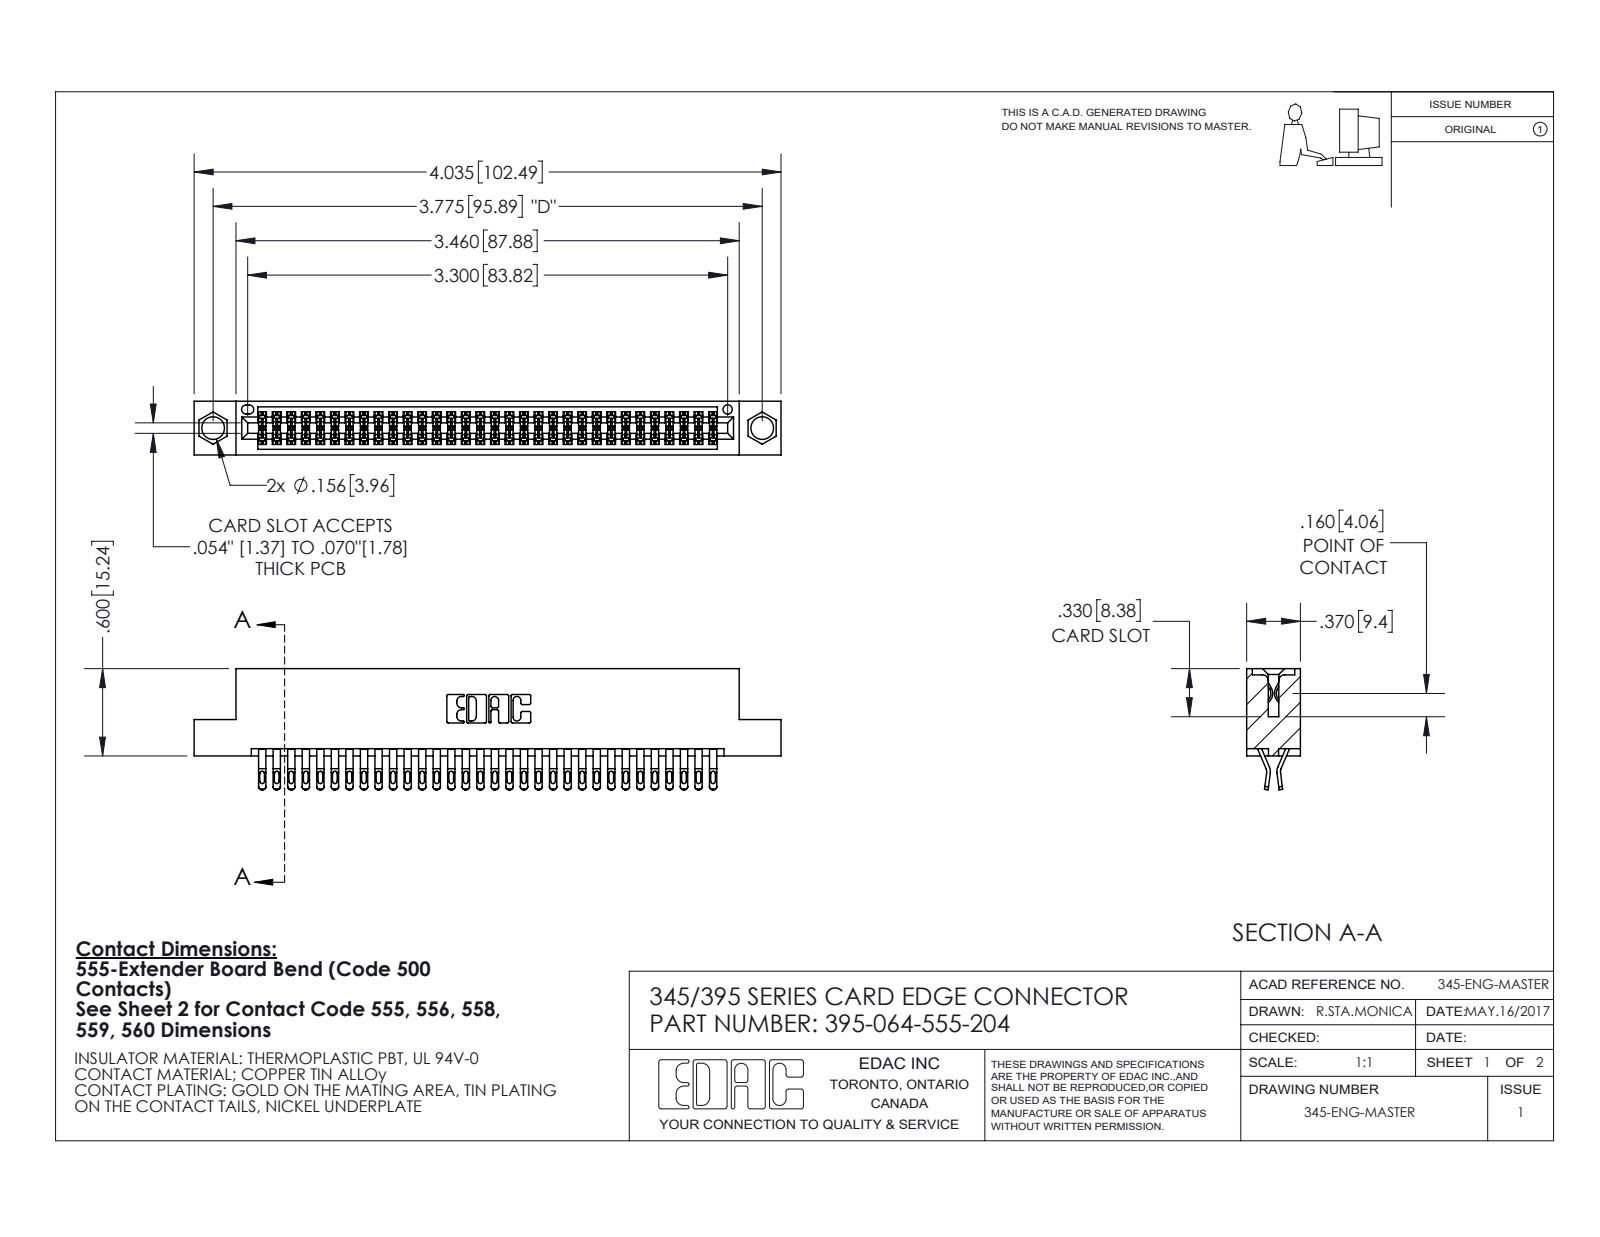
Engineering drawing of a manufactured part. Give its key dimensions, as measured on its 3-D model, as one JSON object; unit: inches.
{"part_name": "395-064-555-204; 345-292-001_555 Tail; 345 Part_Flush Mounting Lugs - 0.156 Dia-TI", "step_written_by": "SolidWorks 2020 (CONFIG_CONTROL_DESIGN)", "units": "inches", "bodies": {"solids": 65, "faces": 3724, "planar": 2078, "cylindrical": 1646, "other": 0}, "overall_size": [4.035, 0.832, 0.37], "volume_in3": 0.607, "surface_area_in2": 23.25, "round_holes": [[0.156, 2], [0.064, 1]], "partial_cylinders_radius": [[0.016, 160], [0.02, 128], [0.006, 96], [0.01, 22], [0.007, 6], [0.031, 6], [0.026, 3], [0.01, 2]], "face_to_face_distances": [0.298, 0.072, 0.2, 0.37, 0.025, 0.098, 0.272, 0.225, 0.175, 0.149], "hole_center_spacings": [0.27, 3.54, 3.775]}
